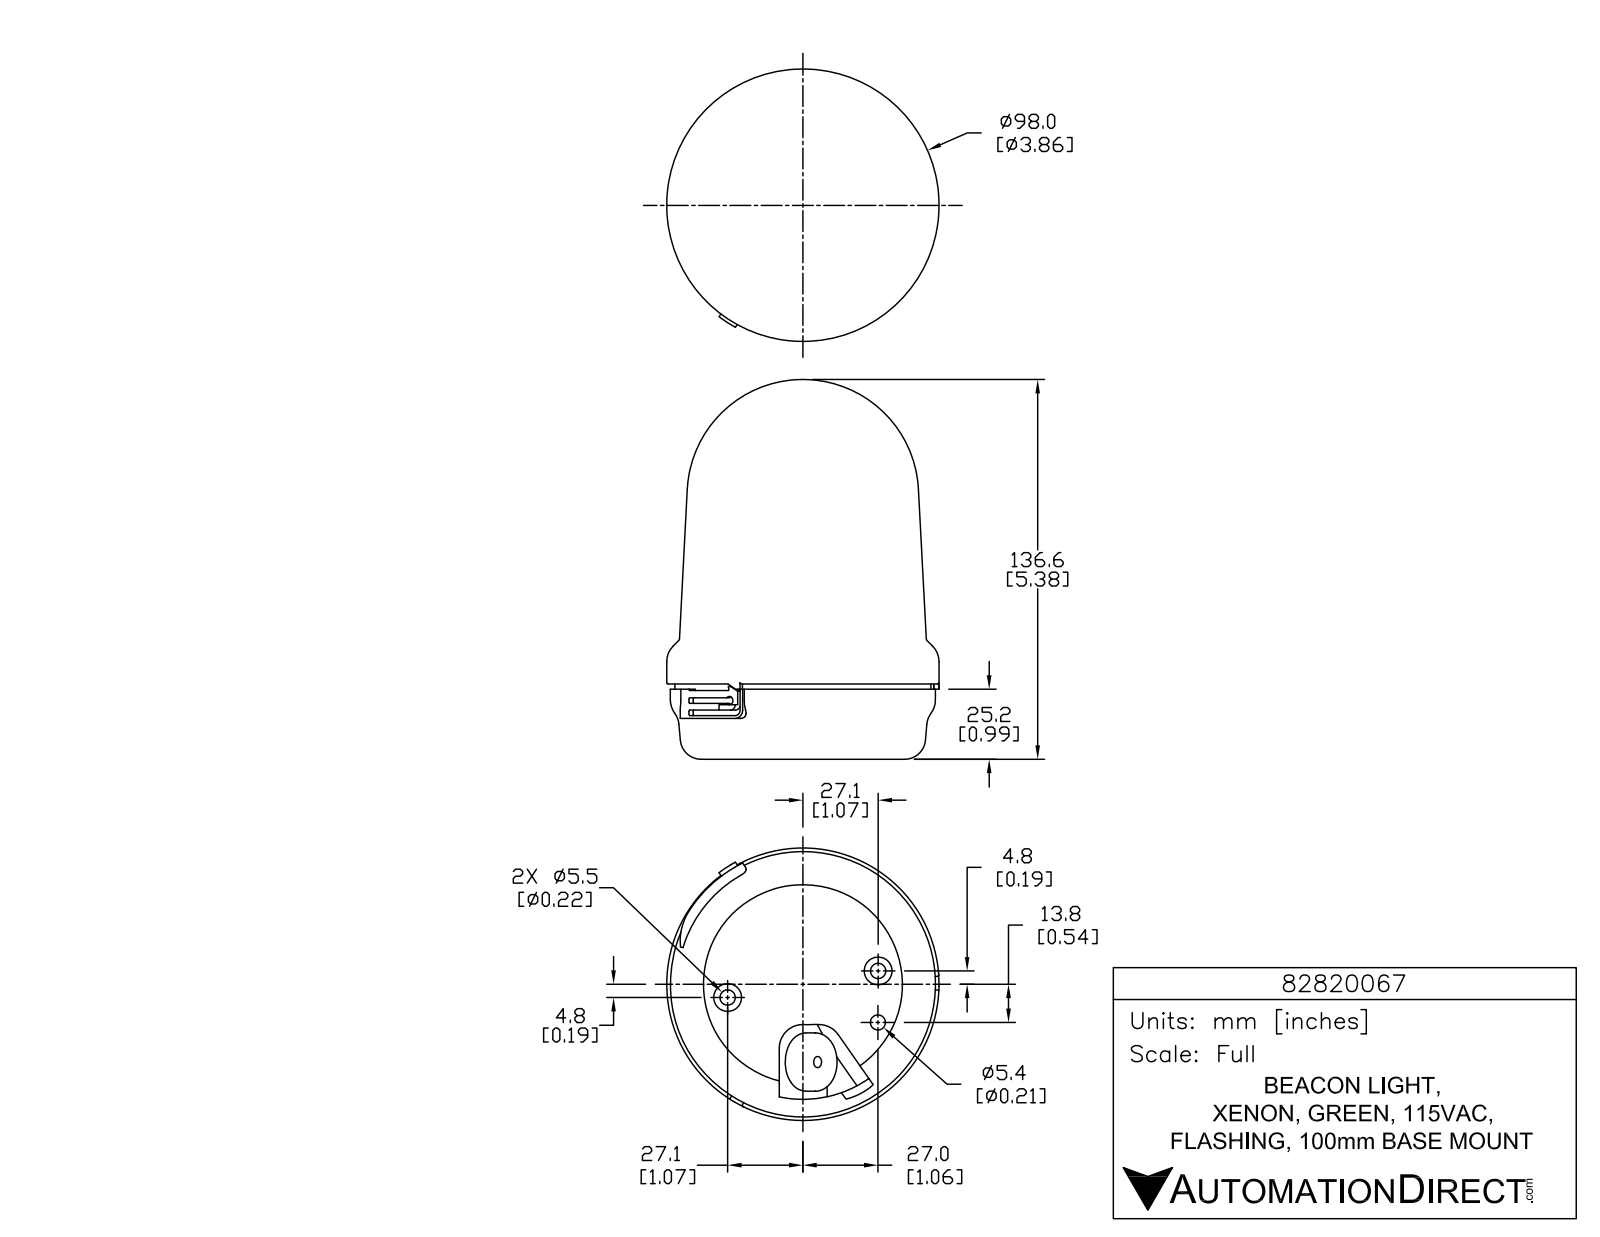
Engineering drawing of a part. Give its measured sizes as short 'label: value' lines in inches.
name: 82820067
written by: SolidWorks 2015 (AUTOMOTIVE_DESIGN)
unit: in
bodies: 1 solid, 872 faces (566 planar, 204 cylindrical, 102 other)
size: 5.378 × 3.858 × 3.858
volume: 44.69 in³; area: 73.66 in²
holes: 3× ⌀0.059, 2× ⌀0.217, 1× ⌀0.157, 1× ⌀0.213, 1× ⌀2.819
bosses: 3× ⌀0.339, 3× ⌀0.084, 2× ⌀0.394, 1× ⌀3.858, 1× ⌀3.756, 1× ⌀3.626, 1× ⌀0.827
rounds: 9× R0.005, 6× R0.005, 6× R0.012, 6× R0.012, 6× R0.012, 6× R0.196, 5× R0.02, 4× R0.039
face distances: 1.045, 0.972, 0.073, 0.02, 0.992, 1.065, 0.236, 0.579, 0.559, 0.413
hole spacings: 1.083, 0.73, 1.193, 2.158, 2.165
